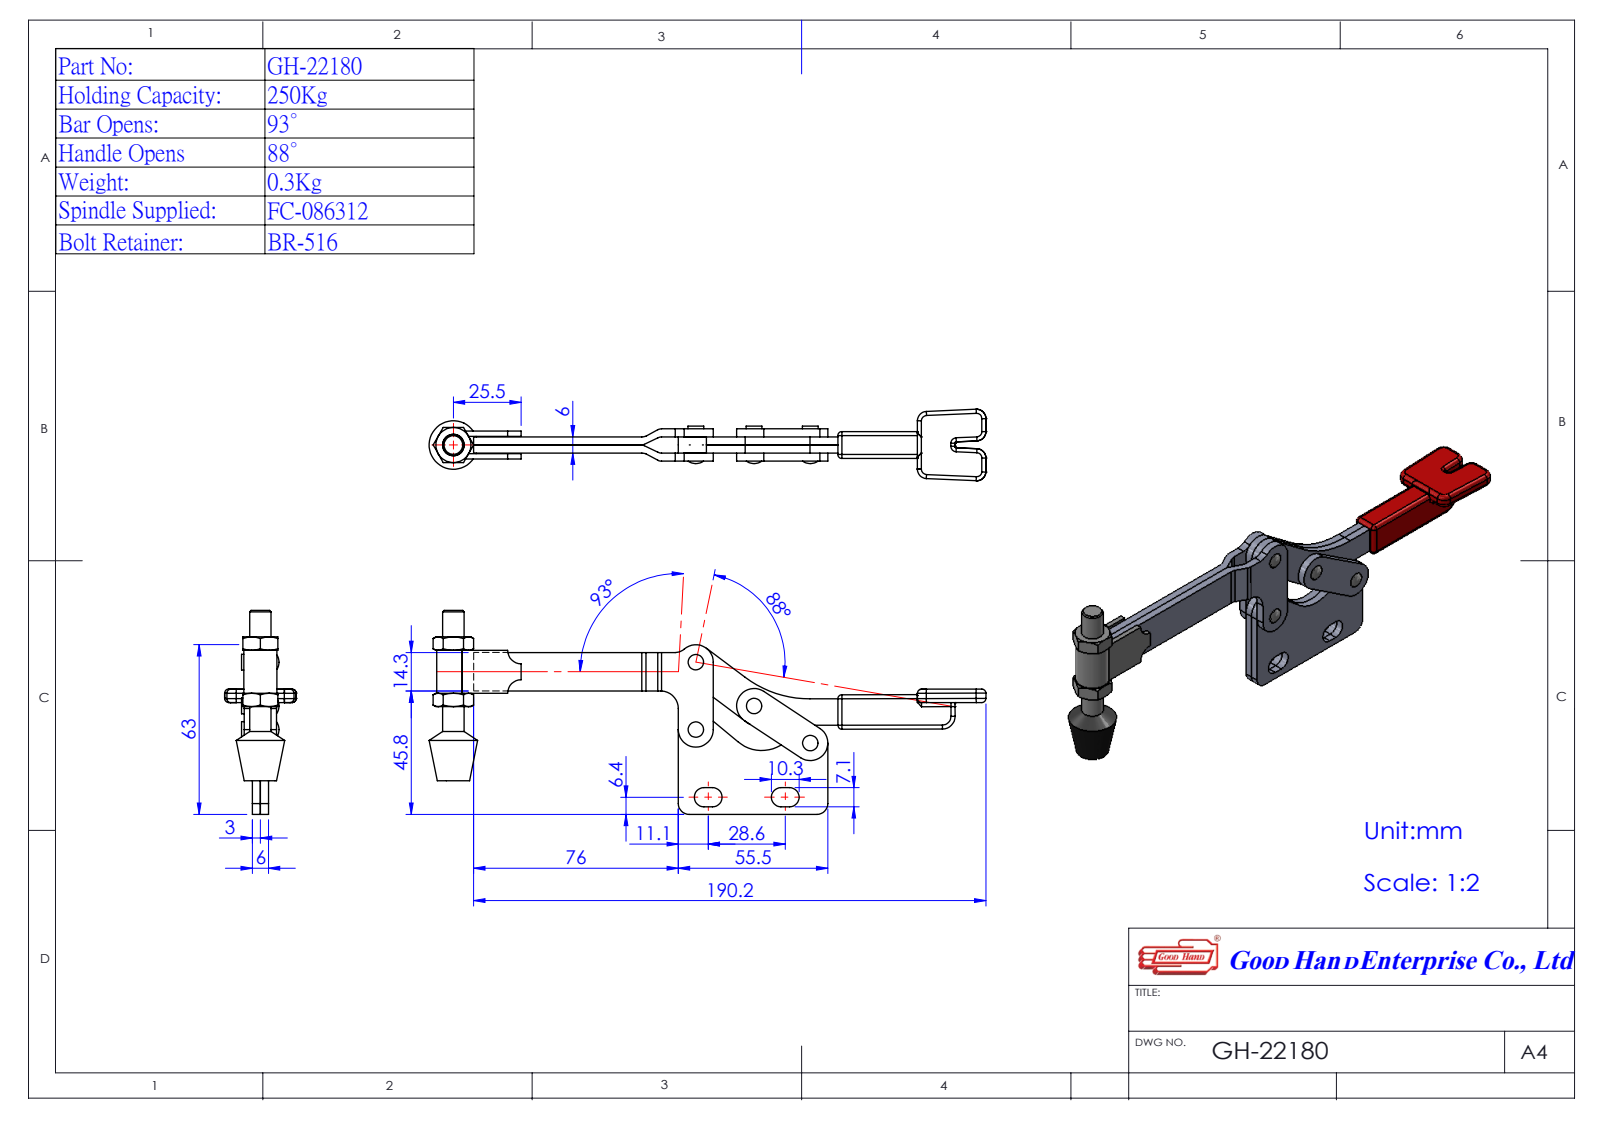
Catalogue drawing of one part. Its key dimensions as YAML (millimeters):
part_name: "GH-22180(簡化)-1; 12216501-1^GH-22180(簡化)-1; Group2^GH-22180(簡化); Group1^GH-22180(簡化) (+2 more)"
step_written_by: "SolidWorks 2016 (AUTOMOTIVE_DESIGN)"
units: millimeters
bodies: {solids: 6, faces: 280, planar: 128, cylindrical: 114, other: 38}
overall_size: [208.09, 75.65, 26.54]
volume: 42887
surface_area: 27512
round_holes:
  - {diameter: 3.5, count: 4}
  - {diameter: 4.83, count: 2}
round_bosses_or_shafts:
  - {diameter: 5.85, count: 4}
  - {diameter: 13, count: 1}
  - {diameter: 7.93, count: 1}
partial_cylinders:
  - {radius: 3.47, count: 6}
  - {radius: 3.55, count: 4}
  - {radius: 6.5, count: 4}
  - {radius: 3, count: 3}
  - {radius: 4.15, count: 3}
  - {radius: 0.53, count: 2}
  - {radius: 2.42, count: 2}
  - {radius: 3.2, count: 2}
face_to_face_distances: [3, 6, 9, 5, 1, 2, 11, 8, 12, 13]
hole_center_spacings: [25, 23.34, 27.05, 42.79, 52.02]
